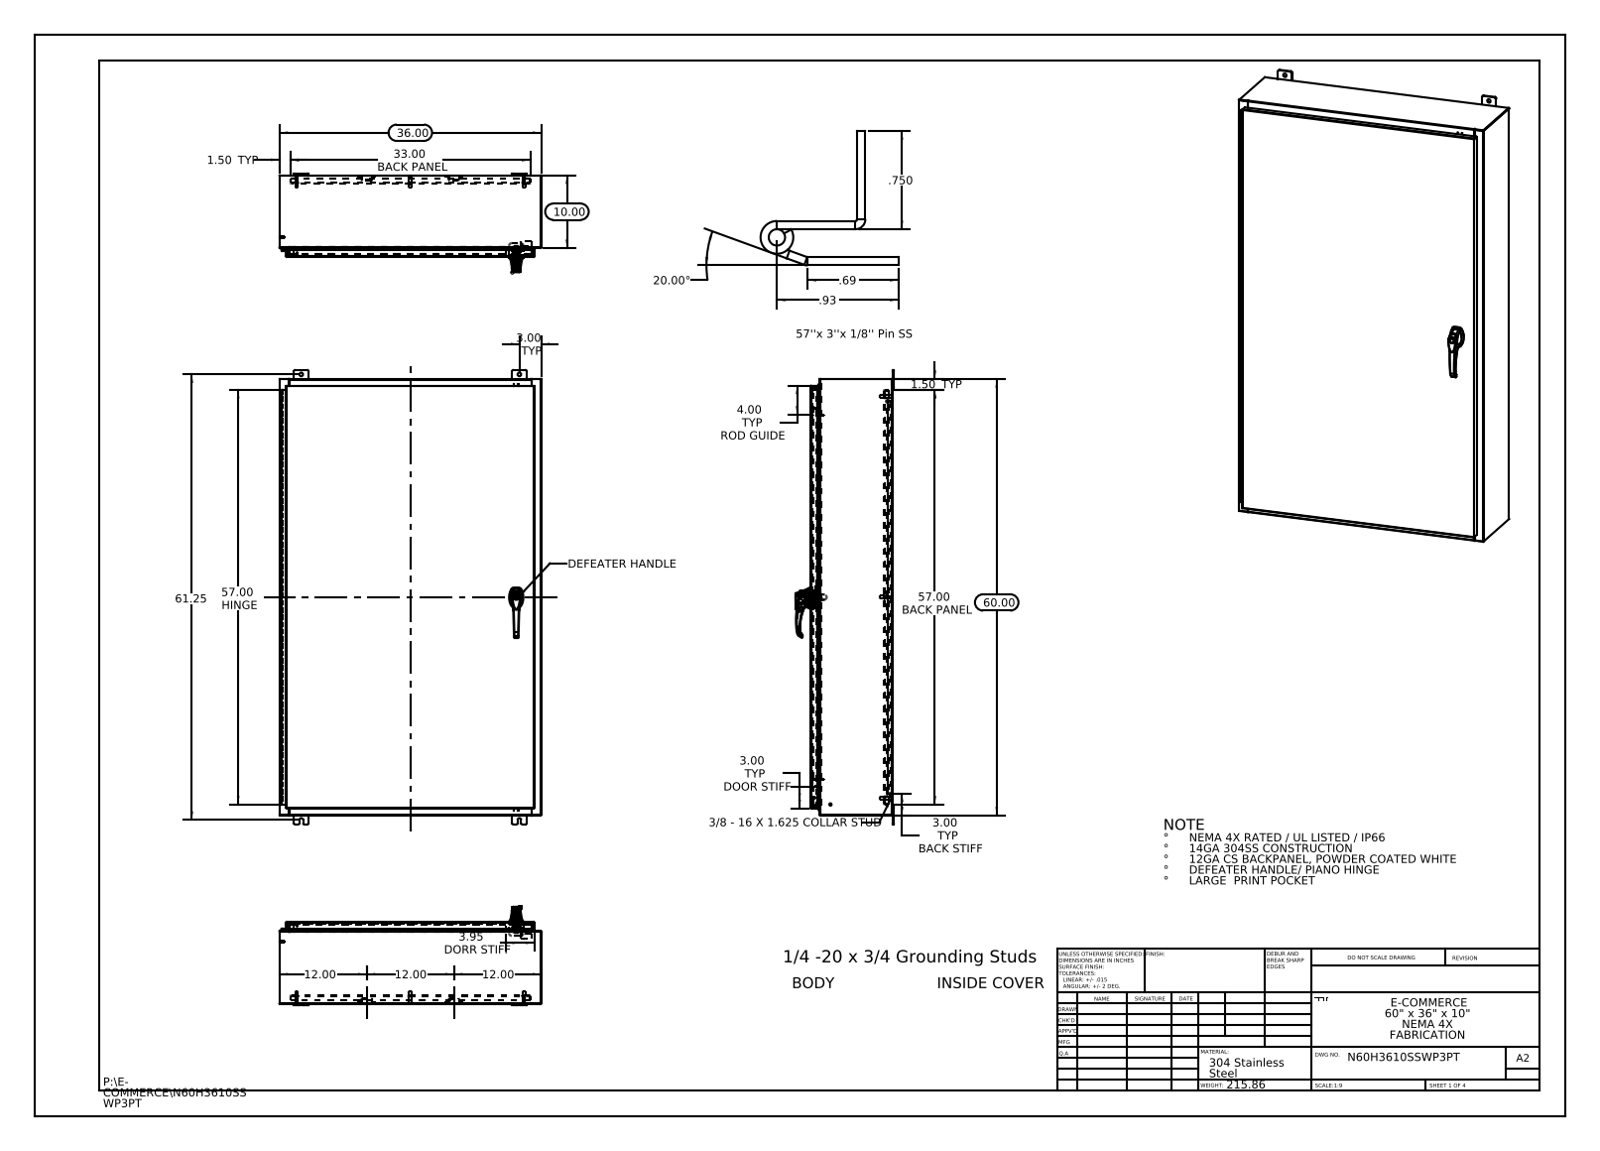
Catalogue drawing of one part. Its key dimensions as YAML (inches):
part_name: "00005090; 26161102; N60H3610SSWP3PT Body; 00005310_26163101 (+8 more)"
step_written_by: "SolidWorks 2013 (CONFIG_CONTROL_DESIGN)"
units: inches
bodies: {solids: 51, faces: 3688, planar: 1453, cylindrical: 1449, other: 786}
overall_size: [62.5, 36, 13.495]
volume: 769.9
surface_area: 19057
round_holes:
  - {diameter: 0.5, count: 12}
  - {diameter: 0.25, count: 10}
  - {diameter: 0.138, count: 3}
  - {diameter: 0.161, count: 3}
  - {diameter: 0.079, count: 2}
  - {diameter: 0.203, count: 2}
  - {diameter: 0.313, count: 2}
  - {diameter: 0.437, count: 2}
  - {diameter: 0.125, count: 1}
  - {diameter: 0.125, count: 1}
  - {diameter: 0.197, count: 1}
  - {diameter: 0.276, count: 1}
round_bosses_or_shafts:
  - {diameter: 0.157, count: 10}
  - {diameter: 0.14, count: 10}
  - {diameter: 0.625, count: 8}
  - {diameter: 0.375, count: 8}
  - {diameter: 0.33, count: 8}
  - {diameter: 0.315, count: 3}
  - {diameter: 0.236, count: 3}
  - {diameter: 1.181, count: 1}
partial_cylinders:
  - {radius: 0.118, count: 37}
  - {radius: 0.013, count: 34}
  - {radius: 0.006, count: 33}
  - {radius: 0.088, count: 28}
  - {radius: 0.19, count: 24}
  - {radius: 0.039, count: 15}
  - {radius: 0.028, count: 12}
  - {radius: 0.008, count: 6}
face_to_face_distances: [0.075, 11.126, 11.051, 0.104, 11.201, 1, 10.126, 1.075, 10.051, 1.179]
hole_center_spacings: [23.354, 25.662, 27.625, 41.709, 57.417, 30.975, 31.25, 55.25]
